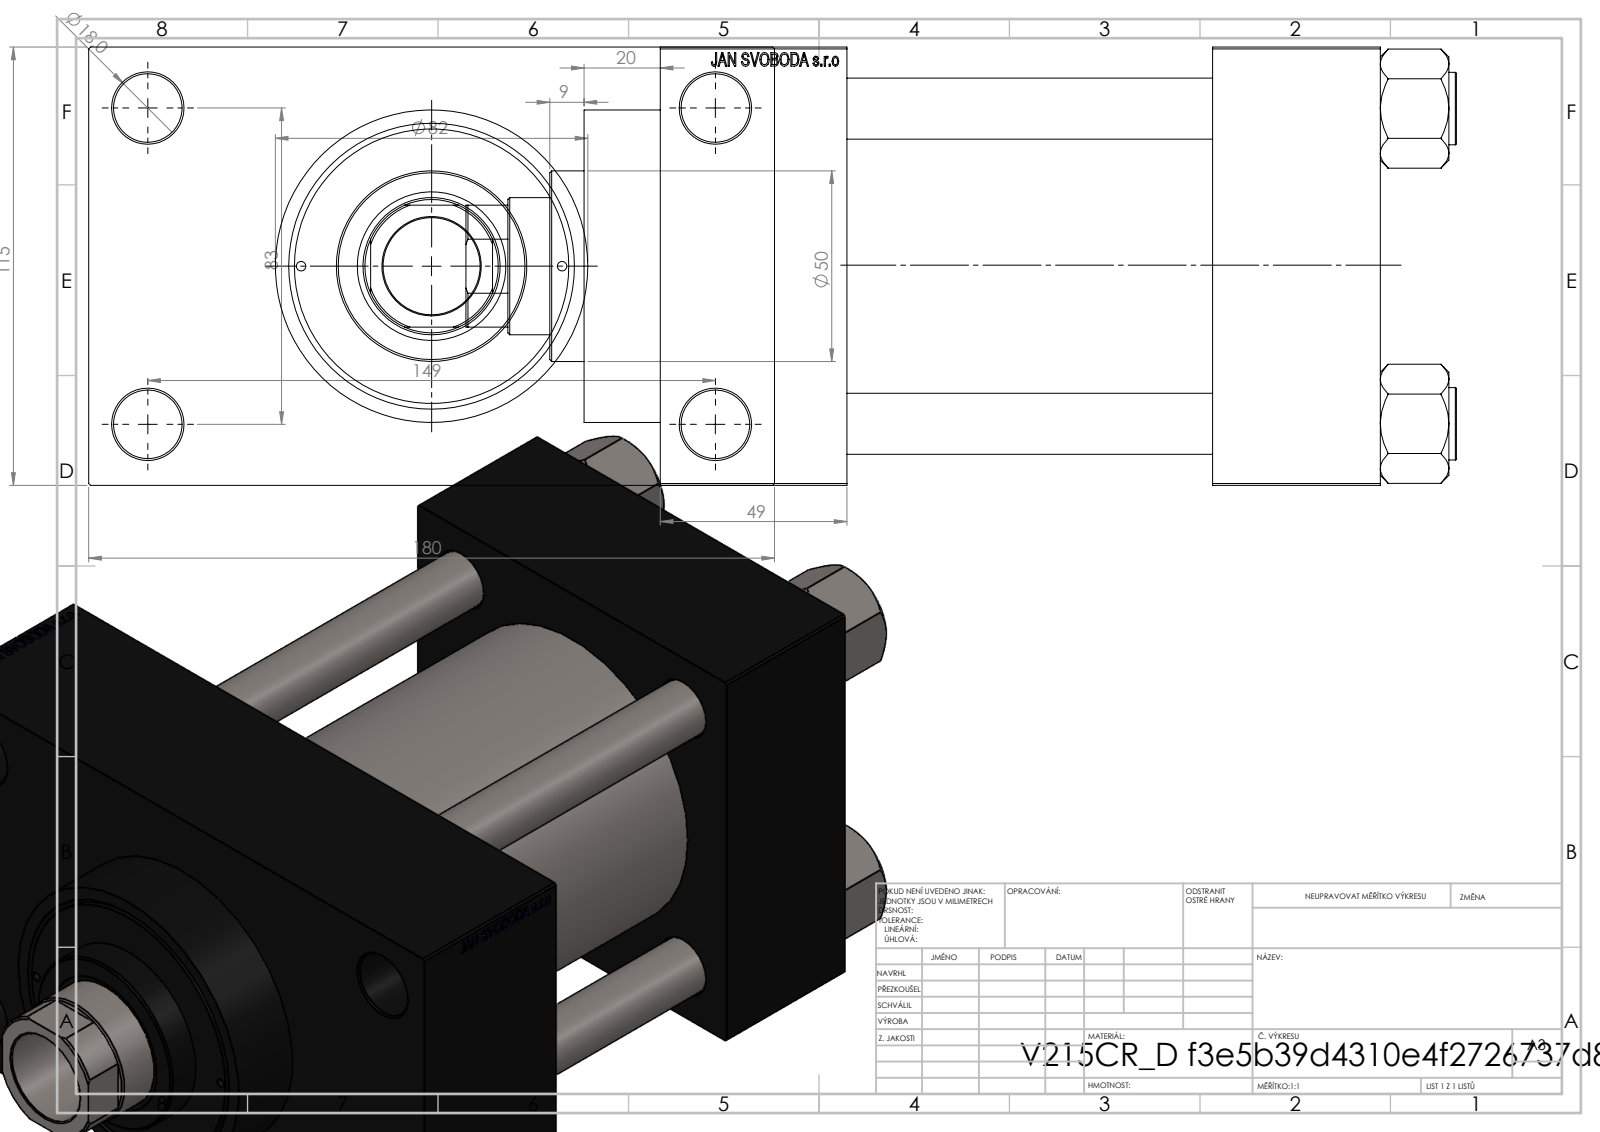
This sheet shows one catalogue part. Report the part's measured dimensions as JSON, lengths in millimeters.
{"part_name": "NUT_M5_D; V215CR_VCP_D; V215_VC_A; V215CR_D_Body (+1 more)", "step_written_by": "SolidWorks 2019 (CONFIG_CONTROL_DESIGN)", "units": "millimeters", "bodies": {"solids": 11, "faces": 1159, "planar": 547, "cylindrical": 92, "other": 520}, "overall_size": [260, 180, 115], "volume_mm3": 2057000, "surface_area_mm2": 321547, "round_holes": [[16, 4], [18, 4], [2.5, 2], [7, 2], [26.44, 2], [35, 2], [25.5, 1], [36, 1], [39, 1], [61, 1], [72, 1], [80, 1]], "round_bosses_or_shafts": [[19, 4], [86, 1], [82, 1], [50, 1]], "partial_cylinders_radius": [[17.5, 1]], "face_to_face_distances": [115, 96, 145, 49, 44, 140, 189, 32.5, 147.5, 180], "hole_center_spacings": [33.15, 41.96, 57.81, 58.48, 82.7, 85.28, 86.17, 89.24]}
